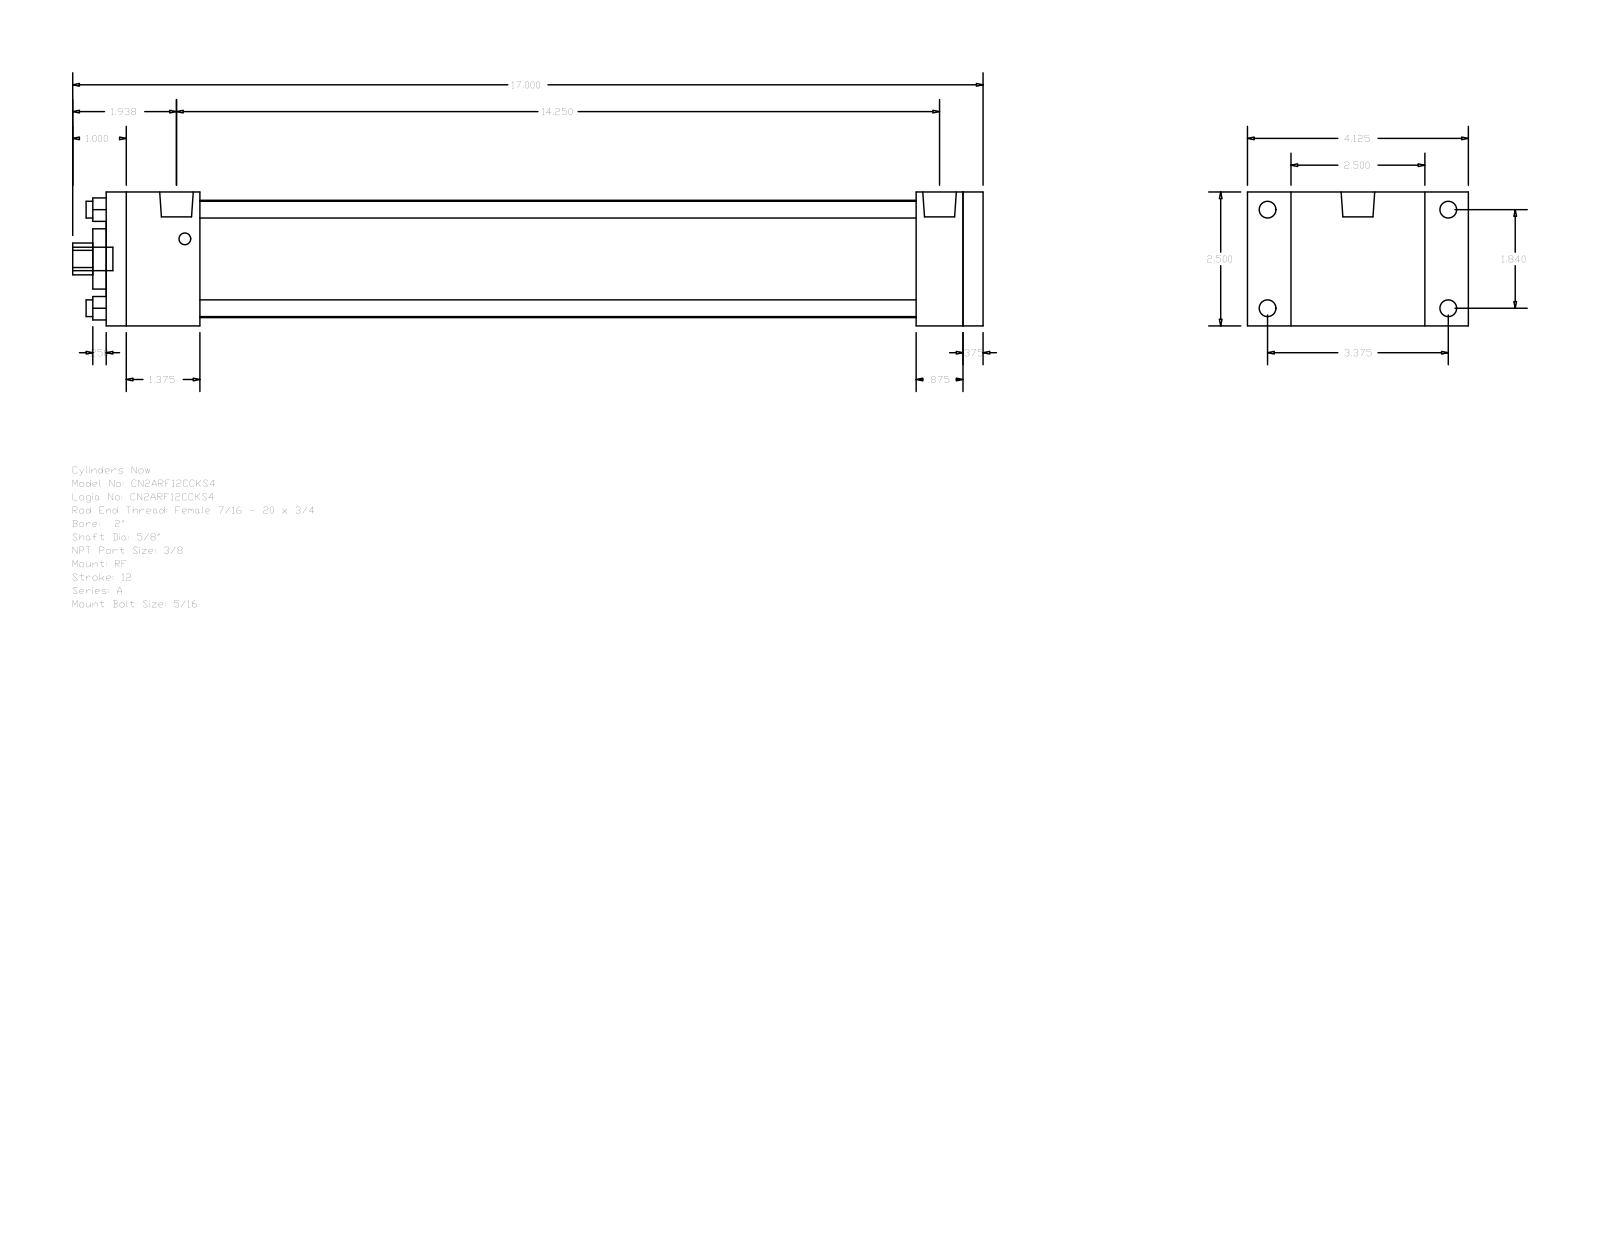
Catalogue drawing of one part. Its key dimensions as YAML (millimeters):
part_name: "A_RF__0200_0.625"
step_written_by: "GSSL Pune (CONFIG_CONTROL_DESIGN)"
units: millimeters
bodies: {solids: 0, faces: 92, planar: 64, cylindrical: 28, other: 0}
overall_size: [431.8, 104.78, 63.5]
round_holes:
  - {diameter: 7.94, count: 4}
  - {diameter: 15.88, count: 1}
  - {diameter: 28.57, count: 1}
  - {diameter: 55.63, count: 1}
round_bosses_or_shafts:
  - {diameter: 7.94, count: 4}
  - {diameter: 5.56, count: 4}
  - {diameter: 15.93, count: 2}
  - {diameter: 11.11, count: 1}
partial_cylinders:
  - {radius: 7.54, count: 1}
face_to_face_distances: [63.5, 415.92, 9.53, 406.39, 44.45, 361.94, 371.47, 384.17, 339.72, 22.22]
hole_center_spacings: [33.05, 46.74, 66.1]
